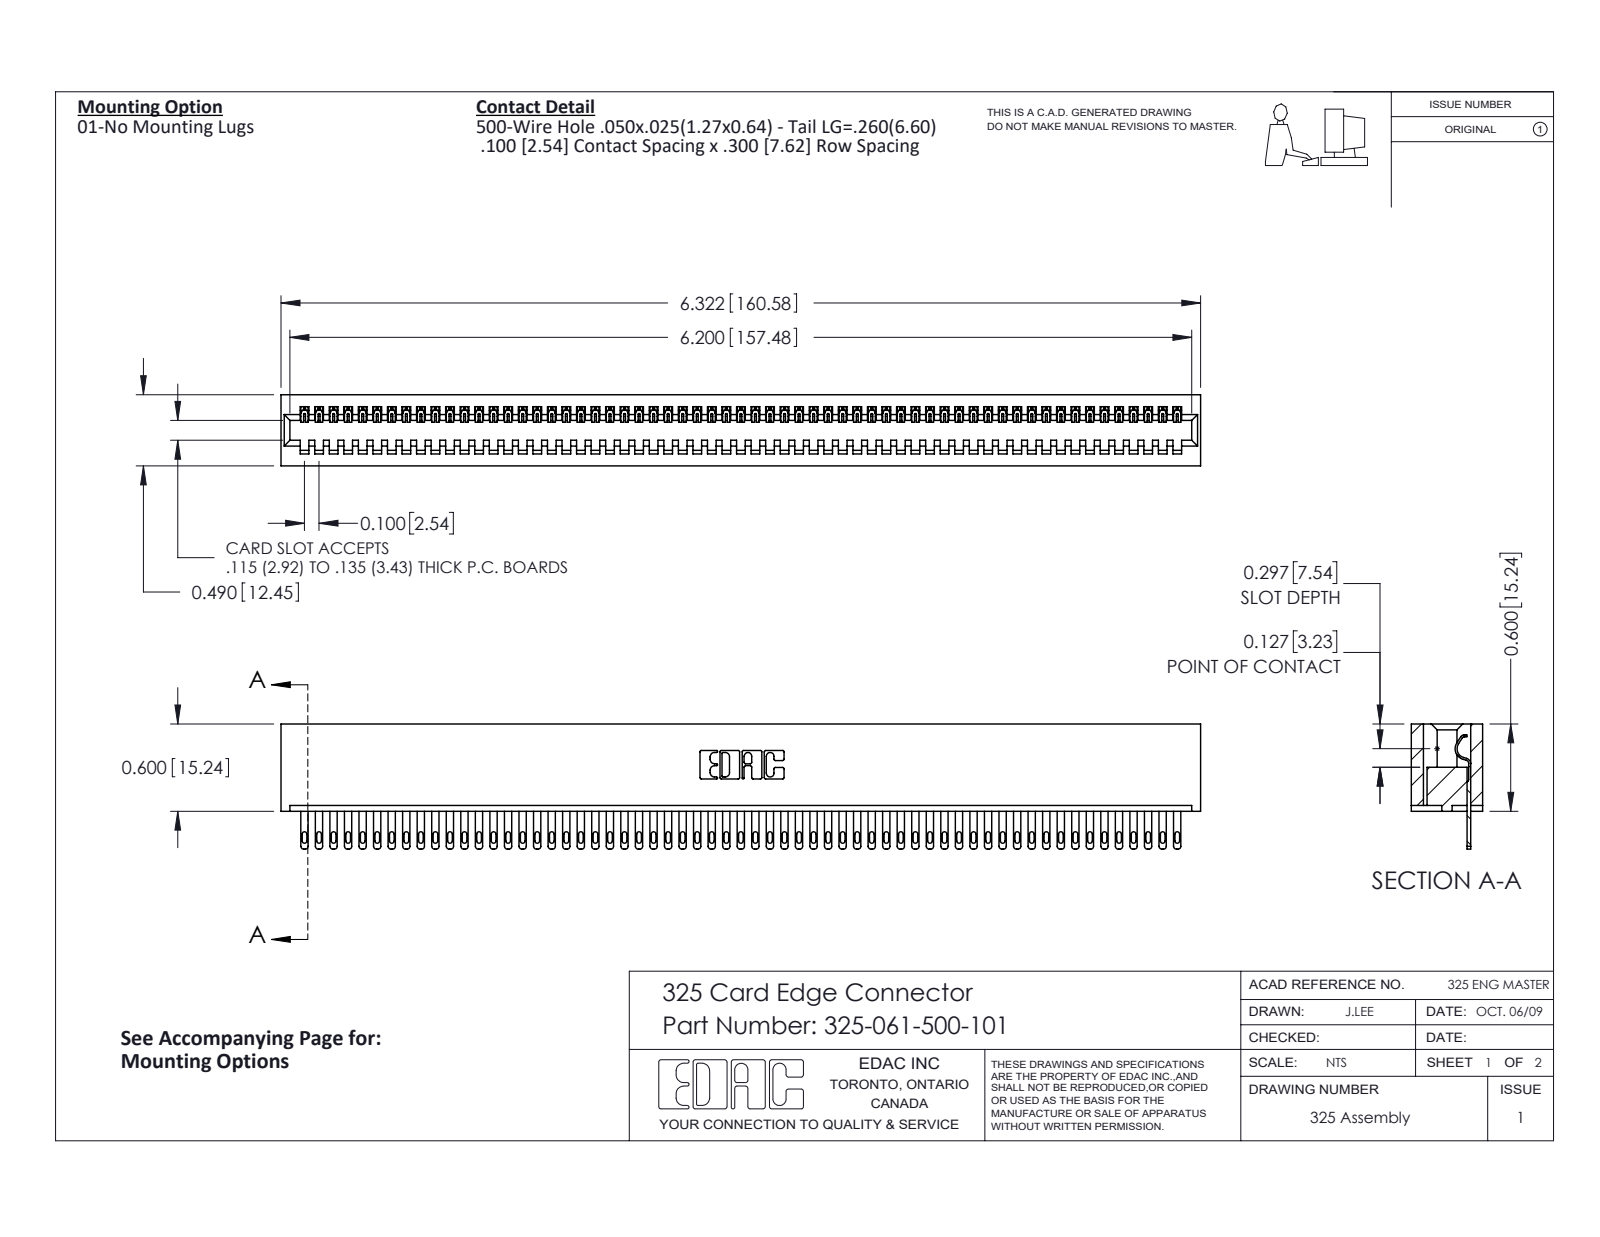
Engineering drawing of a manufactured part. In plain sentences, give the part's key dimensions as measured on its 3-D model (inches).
The part is named "325-061-500-101; 325 Part_Lugless; 325-292-001_325-293-100". Its 3-D file was written by "SolidWorks 2016 (CONFIG_CONTROL_DESIGN)". It is 62 solids with 3400 faces: 2262 planar, 1138 cylindrical and 0 other. Overall it measures 6.322 by 0.86 by 0.49 inches. Its volume is 1.29 cubic inches and its surface area 37.29 square inches. Partial cylindrical surfaces (rounded edges, fillets, slot ends): 122 of radius 0.006, 122 of radius 0.016, 122 of radius 0.02, 22 of radius 0.01, 6 of radius 0.007, 6 of radius 0.031, 3 of radius 0.026, 1 of radius 0.014. The main face-to-face distances are 0.083, 0.407, 0.49, 0.107, 0.383, 0.025, 0.3, 0.325, 0.263, 0.56.
